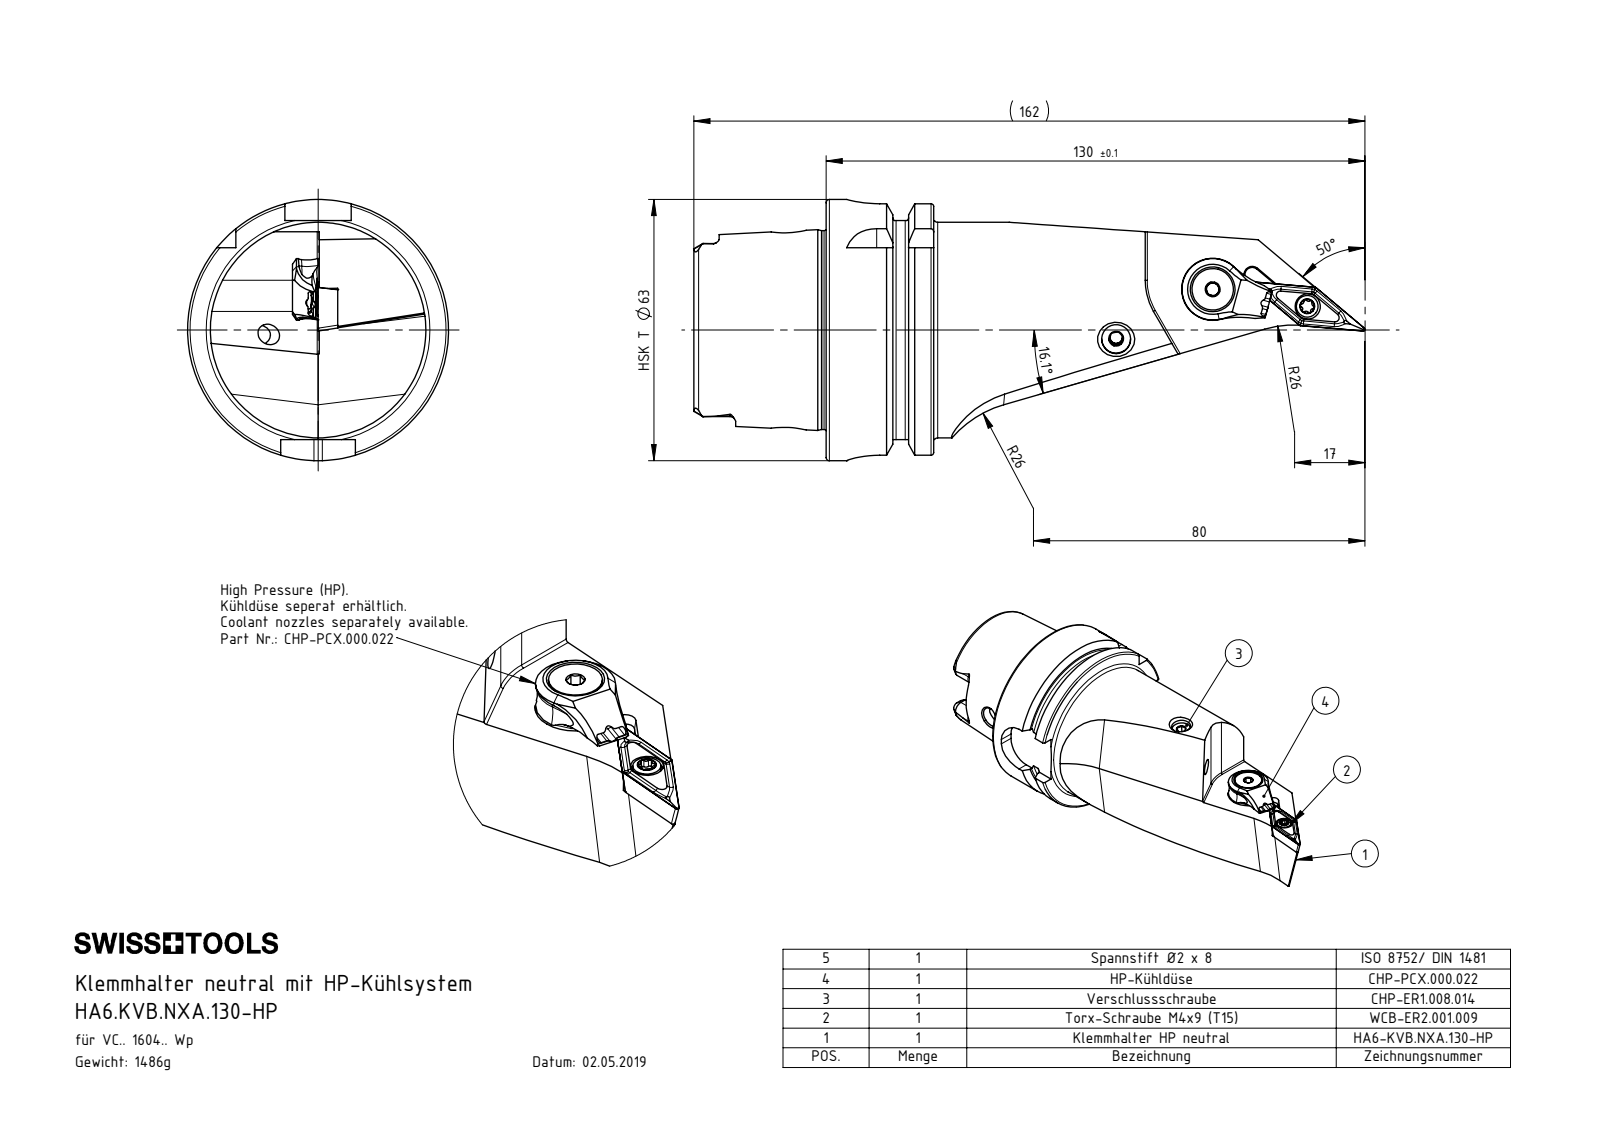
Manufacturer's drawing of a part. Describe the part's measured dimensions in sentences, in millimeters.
The part is named "DIN 7991 - M5x18; DIN 3771 - 13x1; VCMT160404; ISO 8752 2x8 (+7 more)". Its 3-D file was written by "SolidWorks 2017 (CONFIG_CONTROL_DESIGN)". It is 9 solids with 532 faces: 132 planar, 151 cylindrical and 249 other. Overall it measures 161.93 by 63 by 63 millimeters. Its volume is 189 217 cubic millimeters and its surface area 39 283 square millimeters. Round holes: 2 of diameter 4.2, 2 of diameter 5, 1 of diameter 1.2, 1 of diameter 2, 1 of diameter 3, 1 of diameter 3.3, 1 of diameter 4.4, 1 of diameter 5.3, 1 of diameter 6.1, 1 of diameter 7, 1 of diameter 7.5, 1 of diameter 8.5. Round bosses or shafts: 1 of diameter 63, 1 of diameter 54.95, 1 of diameter 52, 1 of diameter 47.94, 1 of diameter 14.85, 1 of diameter 13.4, 1 of diameter 10, 1 of diameter 8. Partial cylindrical surfaces (rounded edges, fillets, slot ends): 7 of radius 1, 6 of radius 0.34, 6 of radius 0.59, 6 of radius 1.4, 4 of radius 0.5, 4 of radius 2.88, 4 of radius 8, 3 of radius 6. The main face-to-face distances are 25.95, 16, 9.95, 31.9, 41.85, 57.85, 52.8, 21.8, 11.85, 4.46. The hole center spacings are 4.51, 20.18, 20.3, 23.19, 23.31, 86.85, 89.16, 109.27.
